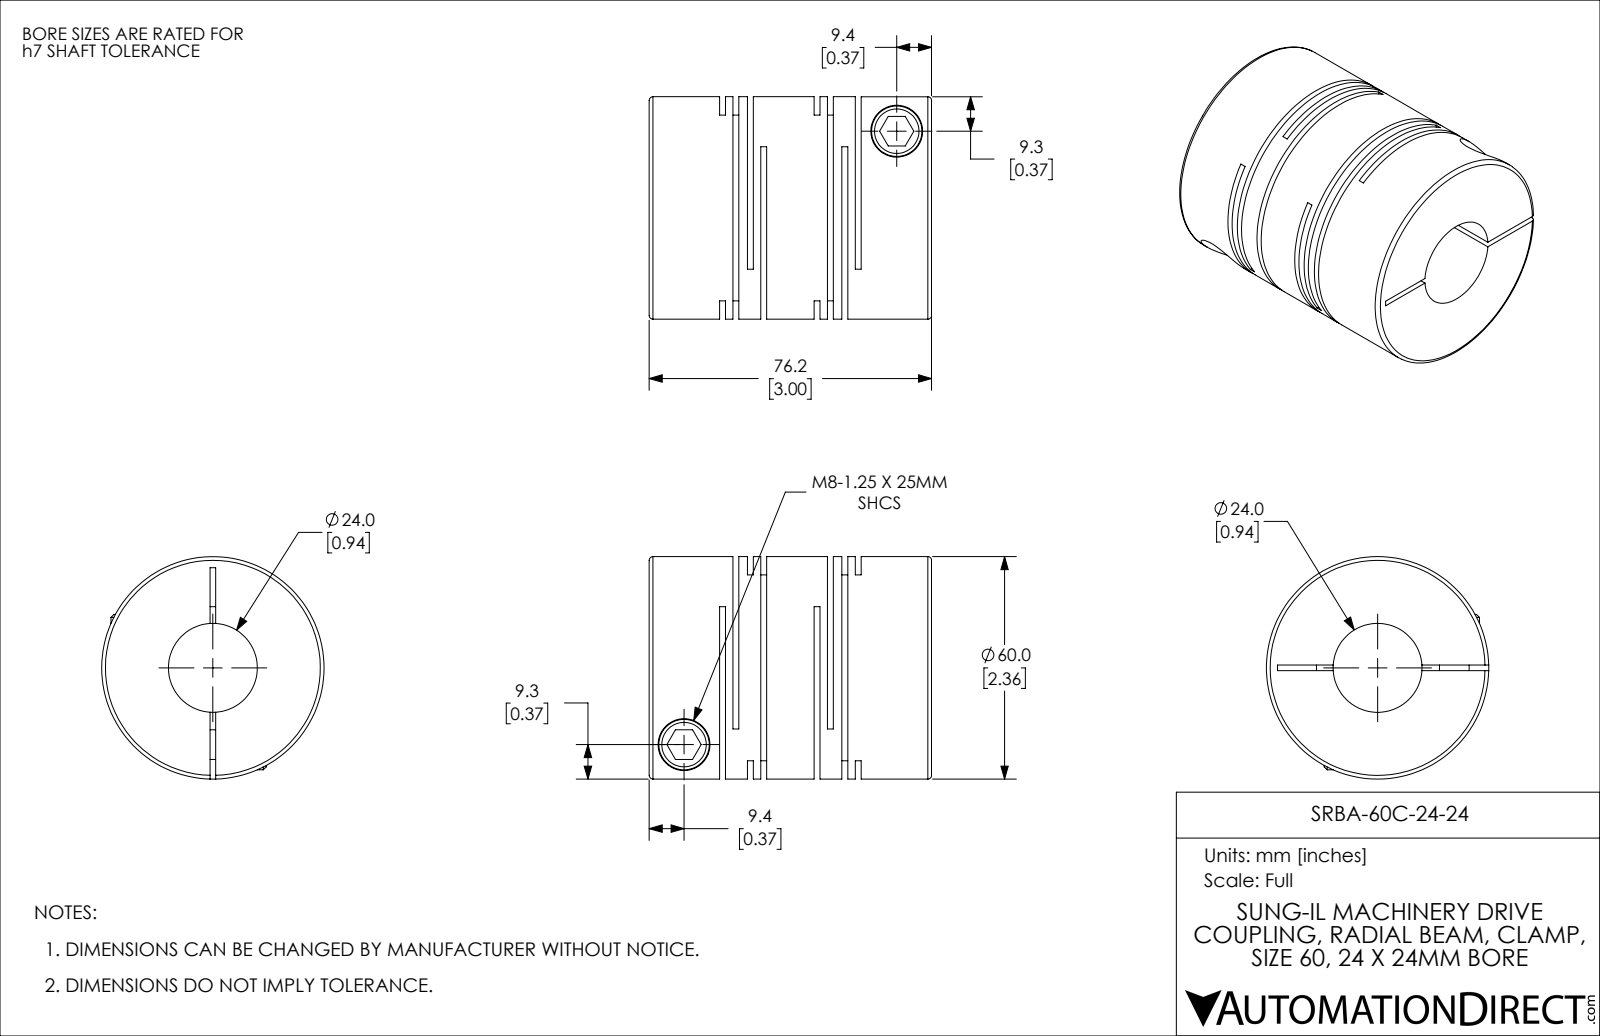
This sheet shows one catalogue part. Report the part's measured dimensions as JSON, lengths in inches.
{"part_name": "SRBA-60C-24-24", "step_written_by": "SolidWorks 2021 (CONFIG_CONTROL_DESIGN)", "units": "inches", "bodies": {"solids": 1, "faces": 115, "planar": 60, "cylindrical": 42, "other": 13}, "overall_size": [3, 2.362, 2.362], "volume_in3": 9.26, "surface_area_in2": 88.58, "round_holes": [[0.315, 2], [0.551, 2], [0.945, 1]], "round_bosses_or_shafts": [[0.535, 2], [2.362, 1]], "face_to_face_distances": [0.063, 0.142, 0.295, 1.004, 1.299, 1.067, 0.232, 0.941, 0.709, 0.079]}
